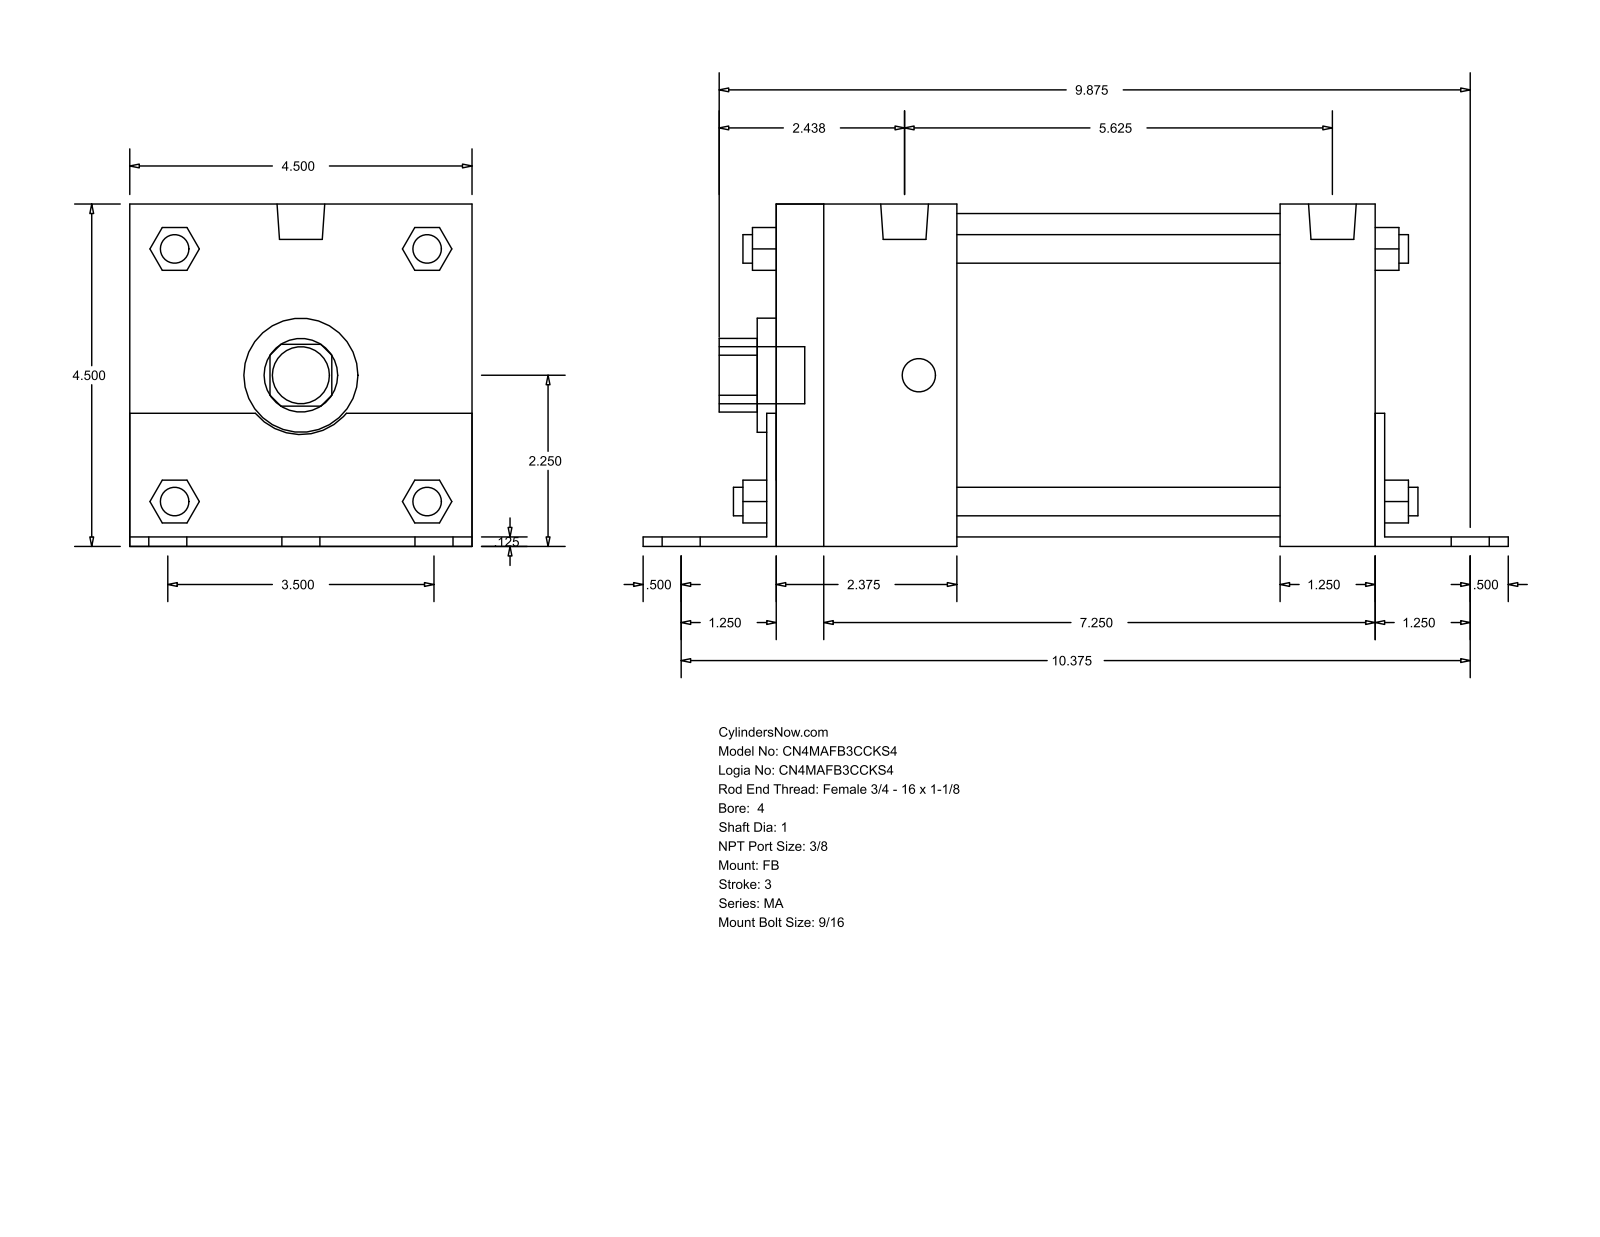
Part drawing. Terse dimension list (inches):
name: MA_FB__0400_1
written by: GSSL Pune (CONFIG_CONTROL_DESIGN)
unit: in
bodies: 0 solids, 140 faces (105 planar, 35 cylindrical, 0 other)
size: 11.375 × 4.502 × 4.5
holes: 1× ⌀1, 1× ⌀1.5, 1× ⌀4.25
bosses: 6× ⌀0.563, 4× ⌀0.437, 4× ⌀0.375, 2× ⌀0.627, 1× ⌀0.75
rounds: 1× R0.484, 1× R0.78
face distances: 4.5, 0.125, 4.502, 0.123, 4.377, 7.875, 0.125, 8.125, 8, 8
